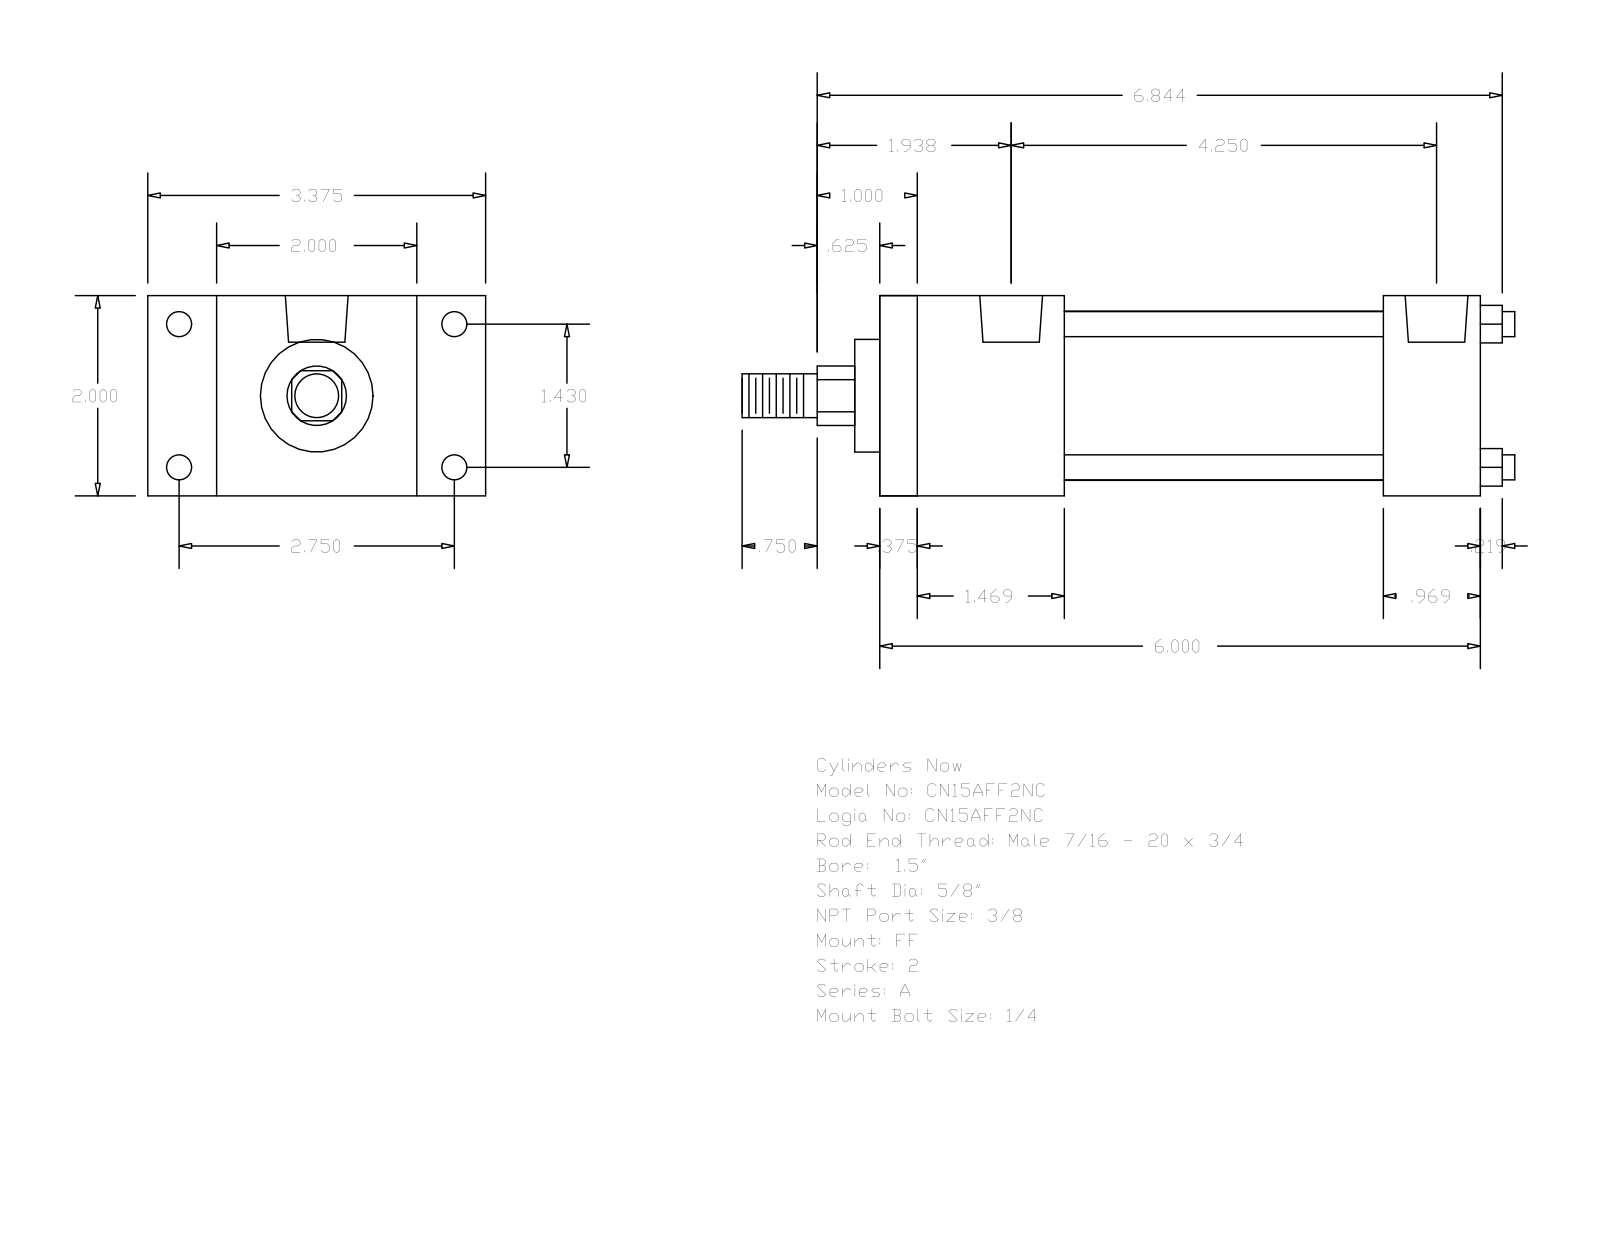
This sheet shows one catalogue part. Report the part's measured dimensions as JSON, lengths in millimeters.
{"part_name": "A_FF__0150_0.625", "step_written_by": "GSSL Pune (CONFIG_CONTROL_DESIGN)", "units": "millimeters", "bodies": {"solids": 0, "faces": 92, "planar": 64, "cylindrical": 28, "other": 0}, "overall_size": [196.06, 85.72, 50.8], "round_holes": [[5.56, 4], [6.35, 4], [15.93, 2]], "round_bosses_or_shafts": [[6.35, 4], [42.93, 1], [28.57, 1], [15.88, 1], [11.11, 1]], "partial_cylinders_radius": [[7.54, 1]], "face_to_face_distances": [50.8, 152.4, 9.52, 142.88, 46.83, 127.79, 37.31, 118.27, 80.96, 105.57], "hole_center_spacings": [3.97, 36.32, 69.84, 78.72, 100.01, 103.98, 107.95]}
